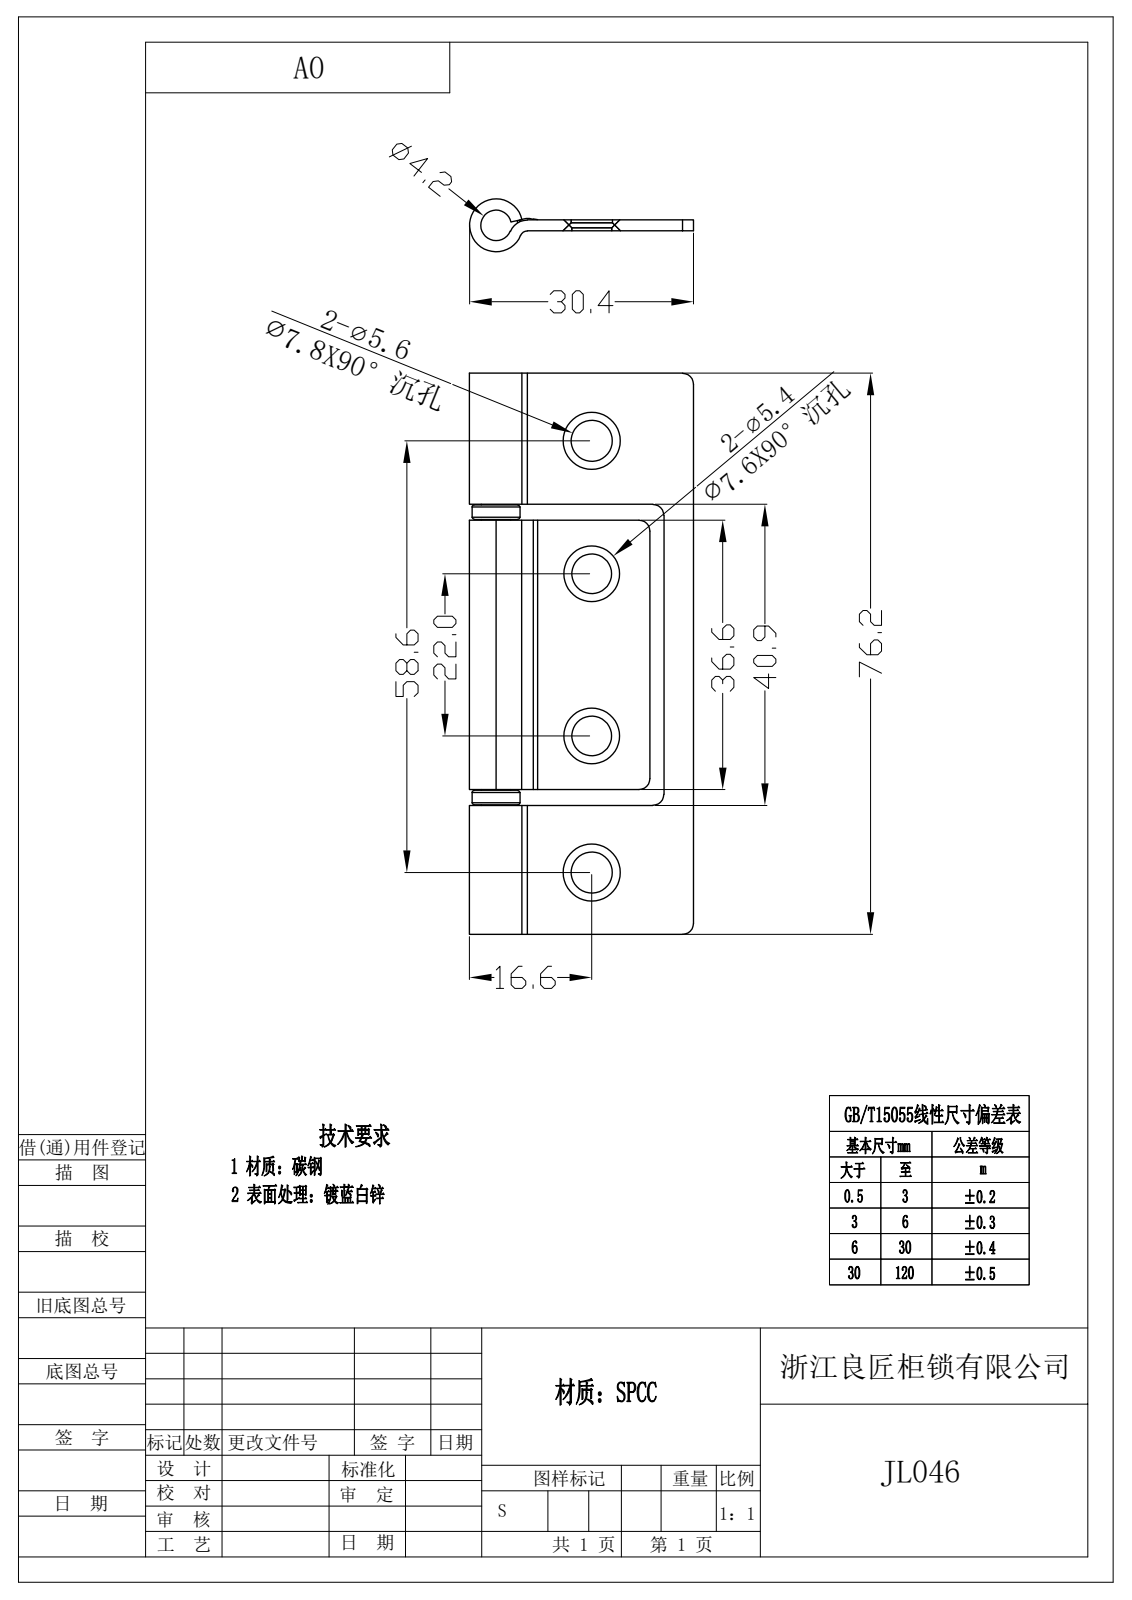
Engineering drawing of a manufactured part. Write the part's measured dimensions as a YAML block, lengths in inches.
step_written_by: "Rhino 8.5 (CONFIG_CONTROL_DESIGN)"
units: inches
bodies: {solids: 4, faces: 81, planar: 24, cylindrical: 41, other: 16}
overall_size: [3, 1.197, 0.283]
volume: 0.311
surface_area: 11.37
round_holes:
  - {diameter: 0.213, count: 2}
  - {diameter: 0.22, count: 2}
  - {diameter: 0.165, count: 1}
round_bosses_or_shafts:
  - {diameter: 0.283, count: 1}
  - {diameter: 0.256, count: 1}
  - {diameter: 0.157, count: 1}
partial_cylinders:
  - {radius: 0.059, count: 6}
  - {radius: 0.039, count: 2}
  - {radius: 0.079, count: 2}
  - {radius: 0.098, count: 2}
face_to_face_distances: [0.059, 1.526, 0.085, 3, 0.157, 0.689, 2.311, 2.299, 1.61, 0.701]
hole_center_spacings: [0.711, 0.73, 0.866, 1.577, 1.596, 2.307]
